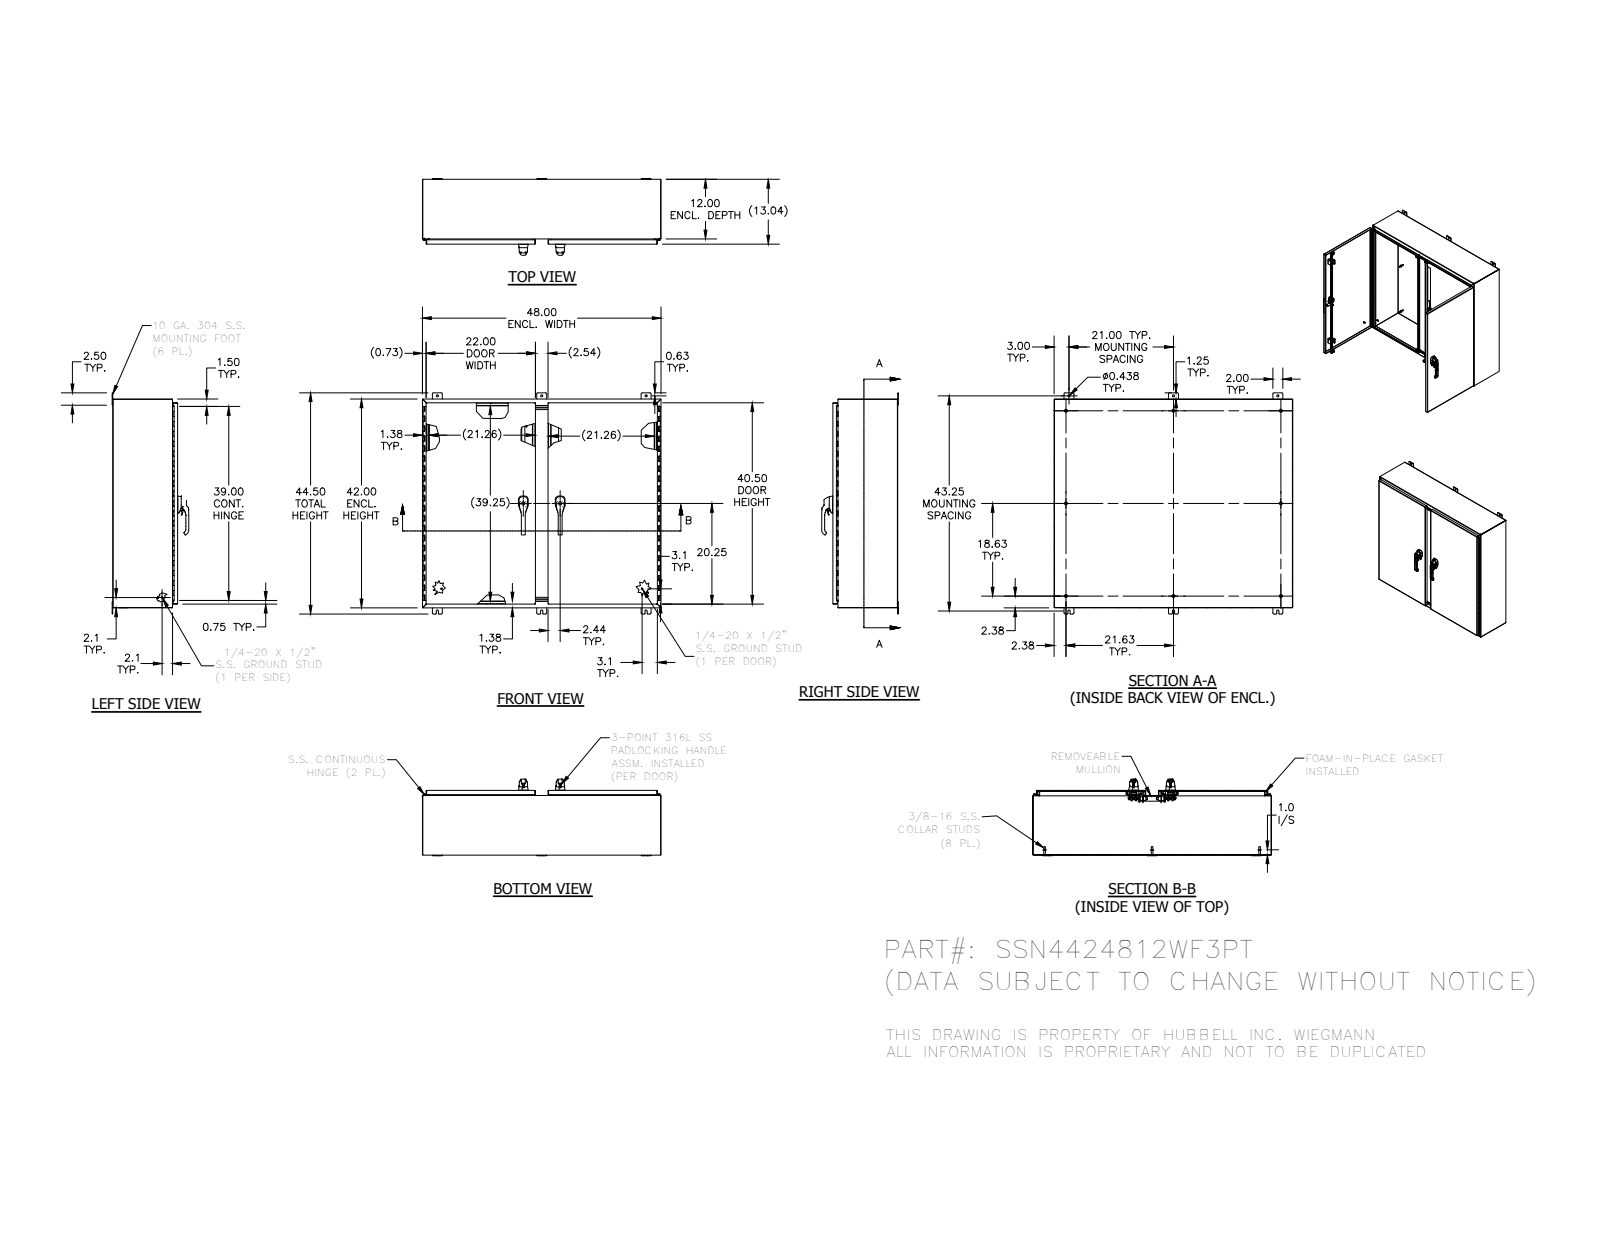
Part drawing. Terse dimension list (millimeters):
name: DIN985_M10; 30254; D125B_10_5; HFW372182 (+8 more)
written by: SolidWorks 2014 (AUTOMOTIVE_DESIGN)
unit: mm
bodies: 127 solids, 6782 faces (2448 planar, 2814 cylindrical, 1520 other)
size: 1219.2 × 1130.3 × 391.4
volume: 9 980 000 mm³; area: 9 750 000 mm²
holes: 12× ⌀6.7, 8× ⌀4.7, 6× ⌀5.4, 6× ⌀7.1, 6× ⌀11.1, 4× ⌀5, 4× ⌀6.4, 4× ⌀7.1, 4× ⌀8, 4× ⌀10.2, 4× ⌀10.2, 4× ⌀11.4
bosses: 9× ⌀6.4, 8× ⌀15.9, 8× ⌀8.4, 6× ⌀13.5, 5× ⌀6, 4× ⌀13.5, 4× ⌀11.1, 4× ⌀11
rounds: 317× R0.5, 221× R0.3, 39× R0.5, 33× R0.8, 31× R3.2, 30× R1.3, 30× R6.4, 25× R2
face distances: 1.9, 2.4, 328.7, 326.8, 331.1, 329.2, 1064.9, 1217.3, 302.9, 1063
hole spacings: 9.7, 19.3, 188.4, 12.5, 12.5, 22.5, 31.4, 35
